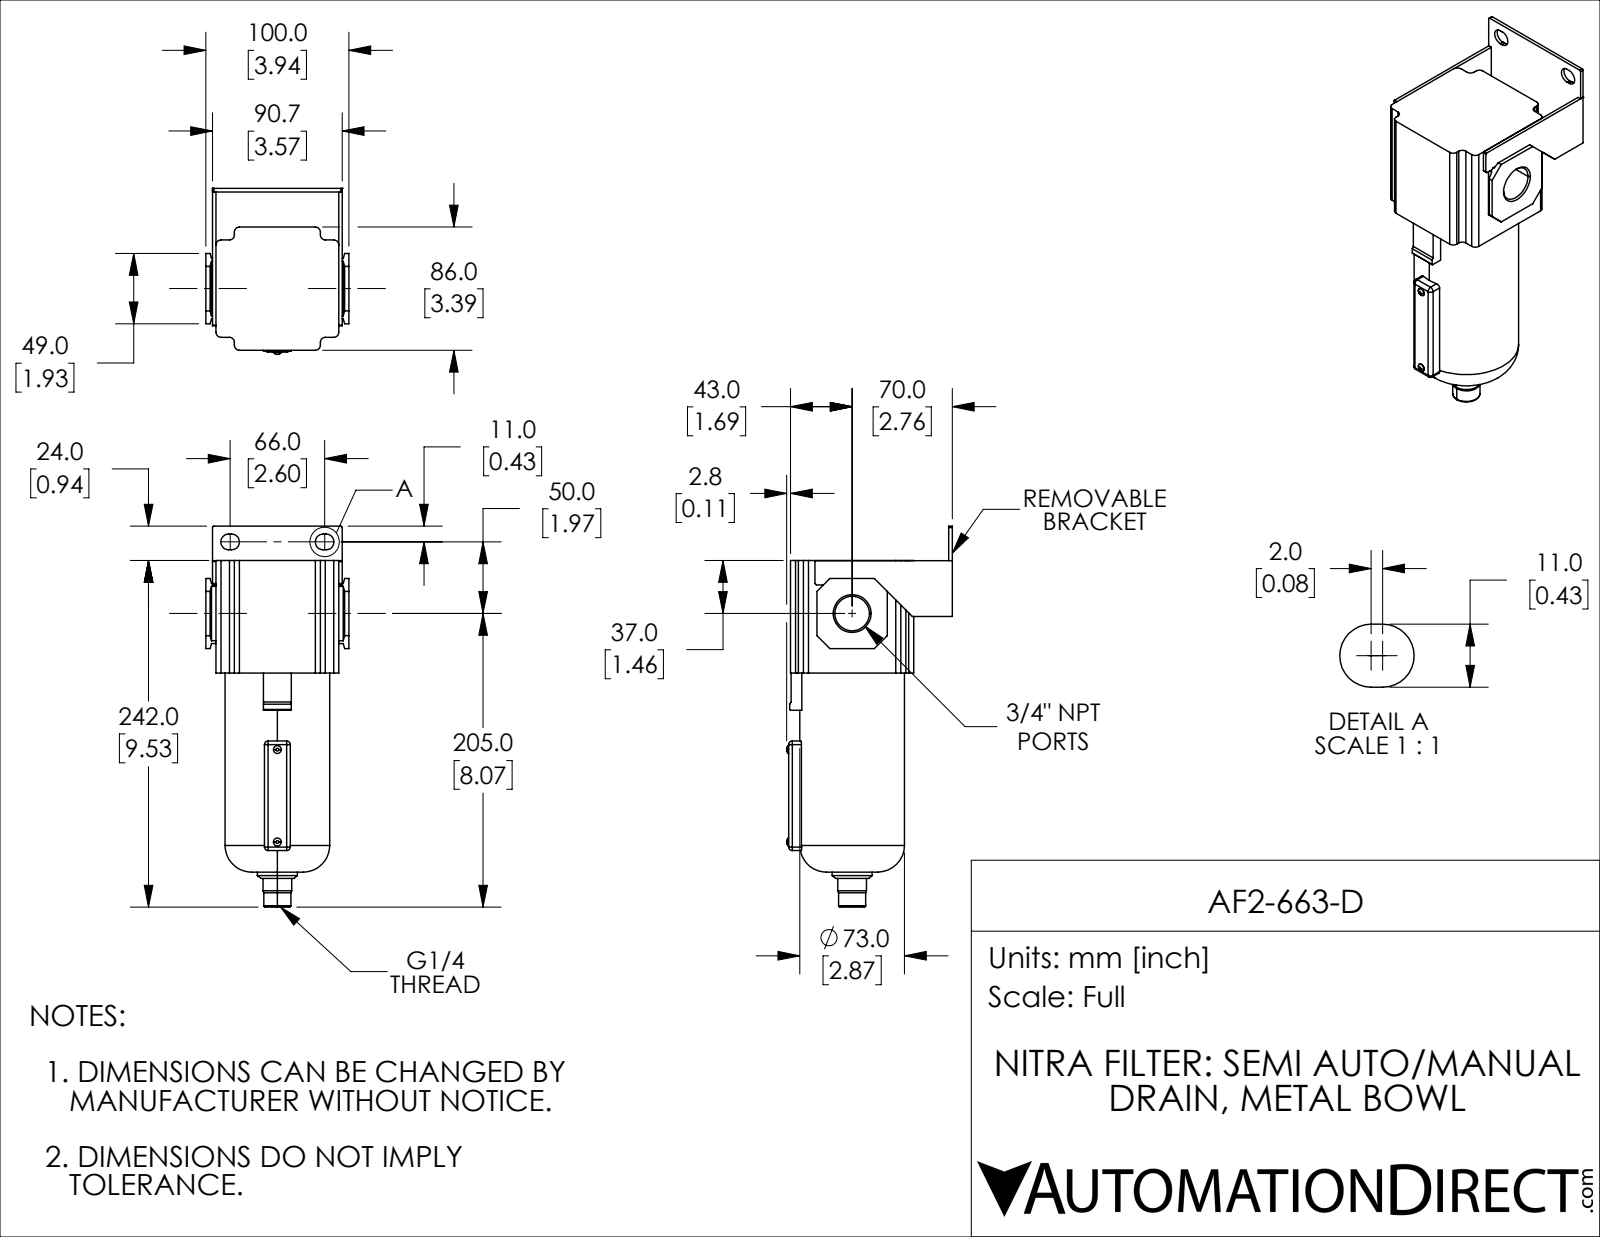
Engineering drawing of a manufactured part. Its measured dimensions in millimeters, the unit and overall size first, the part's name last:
Units: millimetres
Overall size (bounding box): 266 × 115.8 × 100
Round holes (diameter × count): ⌀8.57 ×1, ⌀24.12 ×1
Round bosses / shafts (diameter × count): ⌀5.5 ×2, ⌀73 ×1, ⌀28 ×1, ⌀20 ×1, ⌀19 ×1
Partial cylindrical surfaces — rounded edges, fillets, slot ends (radius × count): R3.5 ×12, R2.5 ×8, R5.5 ×4, R1 ×2
Main face-to-face distances: 2.5, 88.2, 24.5, 113, 86, 27, 110.5, 85.7, 4.65, 7.15
Volume: 1 160 000 mm³ · Surface area: 98 586 mm²
Bodies: 1 solid, 160 faces (94 planar, 44 cylindrical, 22 other)
Part name (STEP PRODUCT): AF2-663-D
STEP written by: SolidWorks 2019 (CONFIG_CONTROL_DESIGN)
